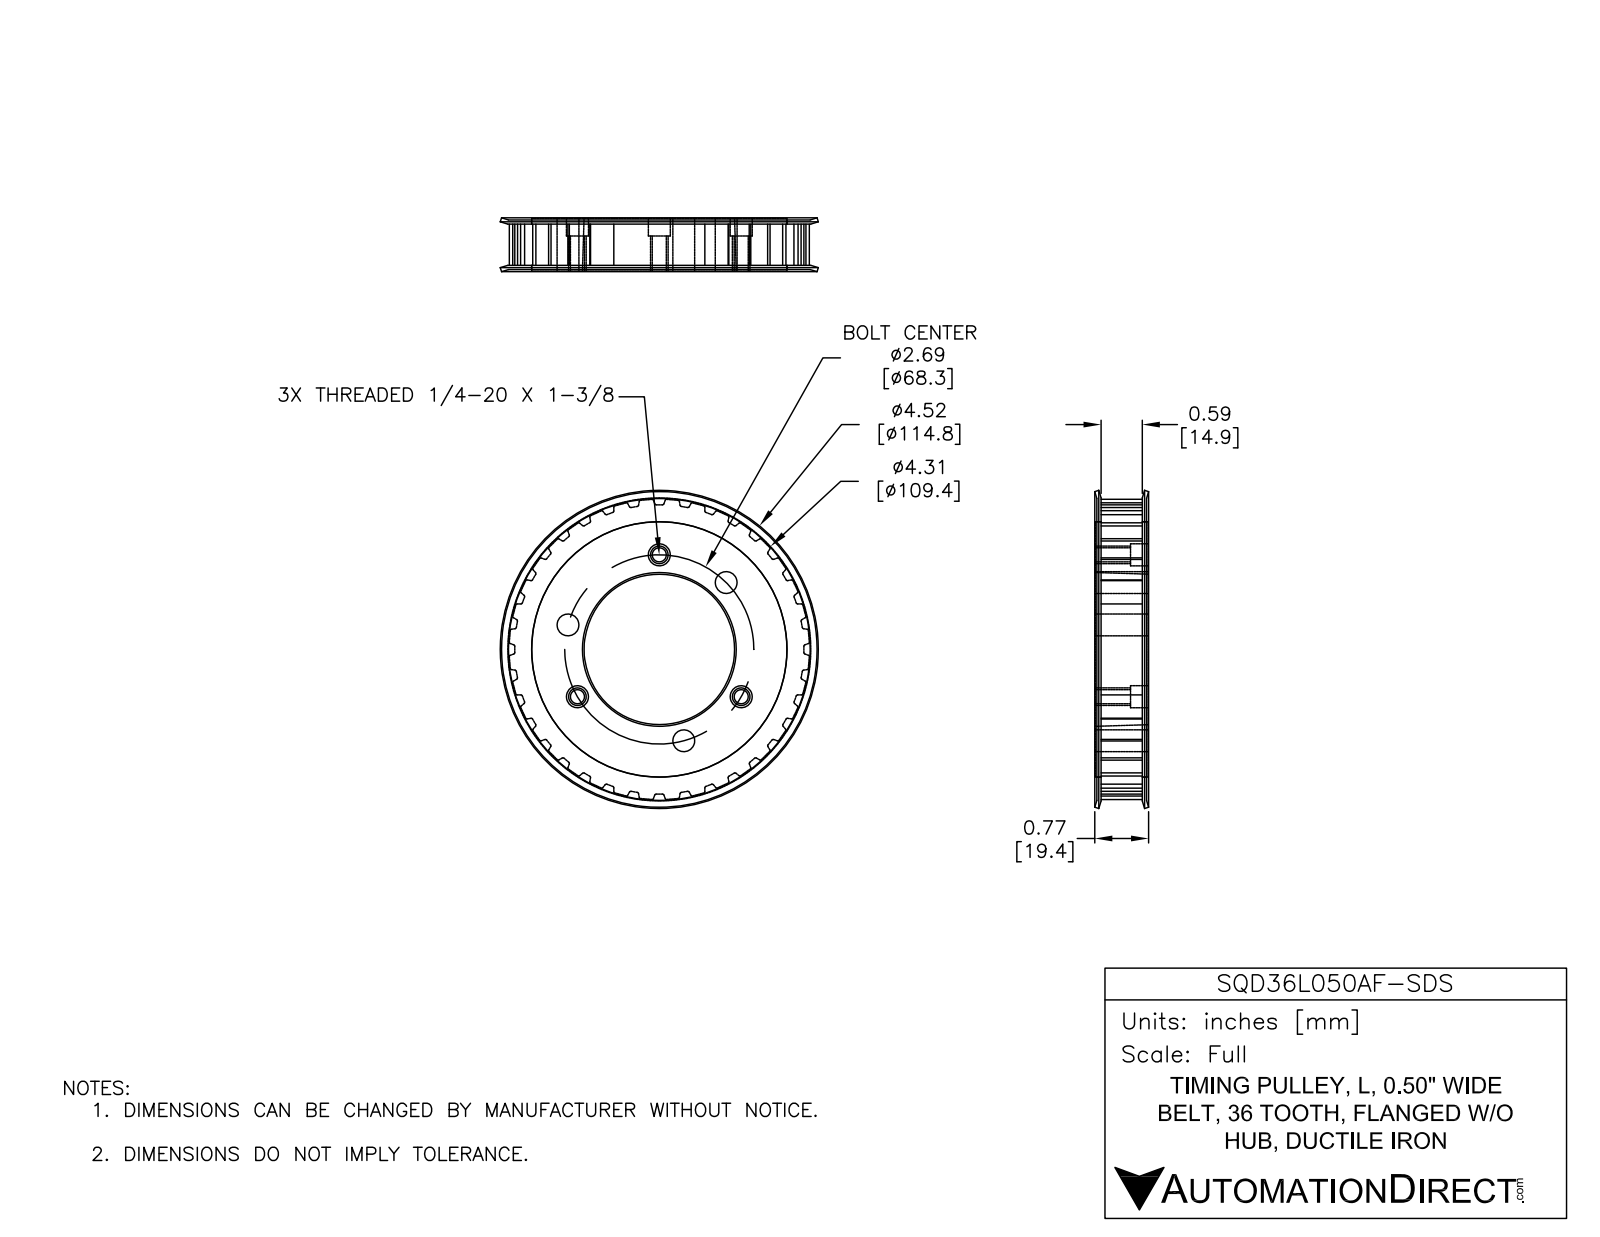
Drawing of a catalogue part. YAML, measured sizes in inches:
part_name: "SQD36L050AF-SDS"
step_written_by: "SolidWorks 2018 (AUTOMOTIVE_DESIGN)"
units: inches
bodies: {solids: 1, faces: 365, planar: 119, cylindrical: 232, other: 14}
overall_size: [4.52, 4.52, 0.765]
volume: 7.479
surface_area: 51.96
round_holes:
  - {diameter: 0.2, count: 3}
  - {diameter: 0.31, count: 3}
  - {diameter: 0.313, count: 3}
  - {diameter: 3.629, count: 1}
round_bosses_or_shafts:
  - {diameter: 3.626, count: 1}
partial_cylinders:
  - {radius: 0.015, count: 72}
  - {radius: 0.02, count: 72}
  - {radius: 2.135, count: 1}
face_to_face_distances: [0.022, 0.728, 0.75, 0.705, 2.701, 1.408, 1.293, 0.083, 0.06, 0.645]
hole_center_spacings: [1.344, 2.327, 1.636, 1.028, 2.328, 2.665, 1.029, 1.343]
